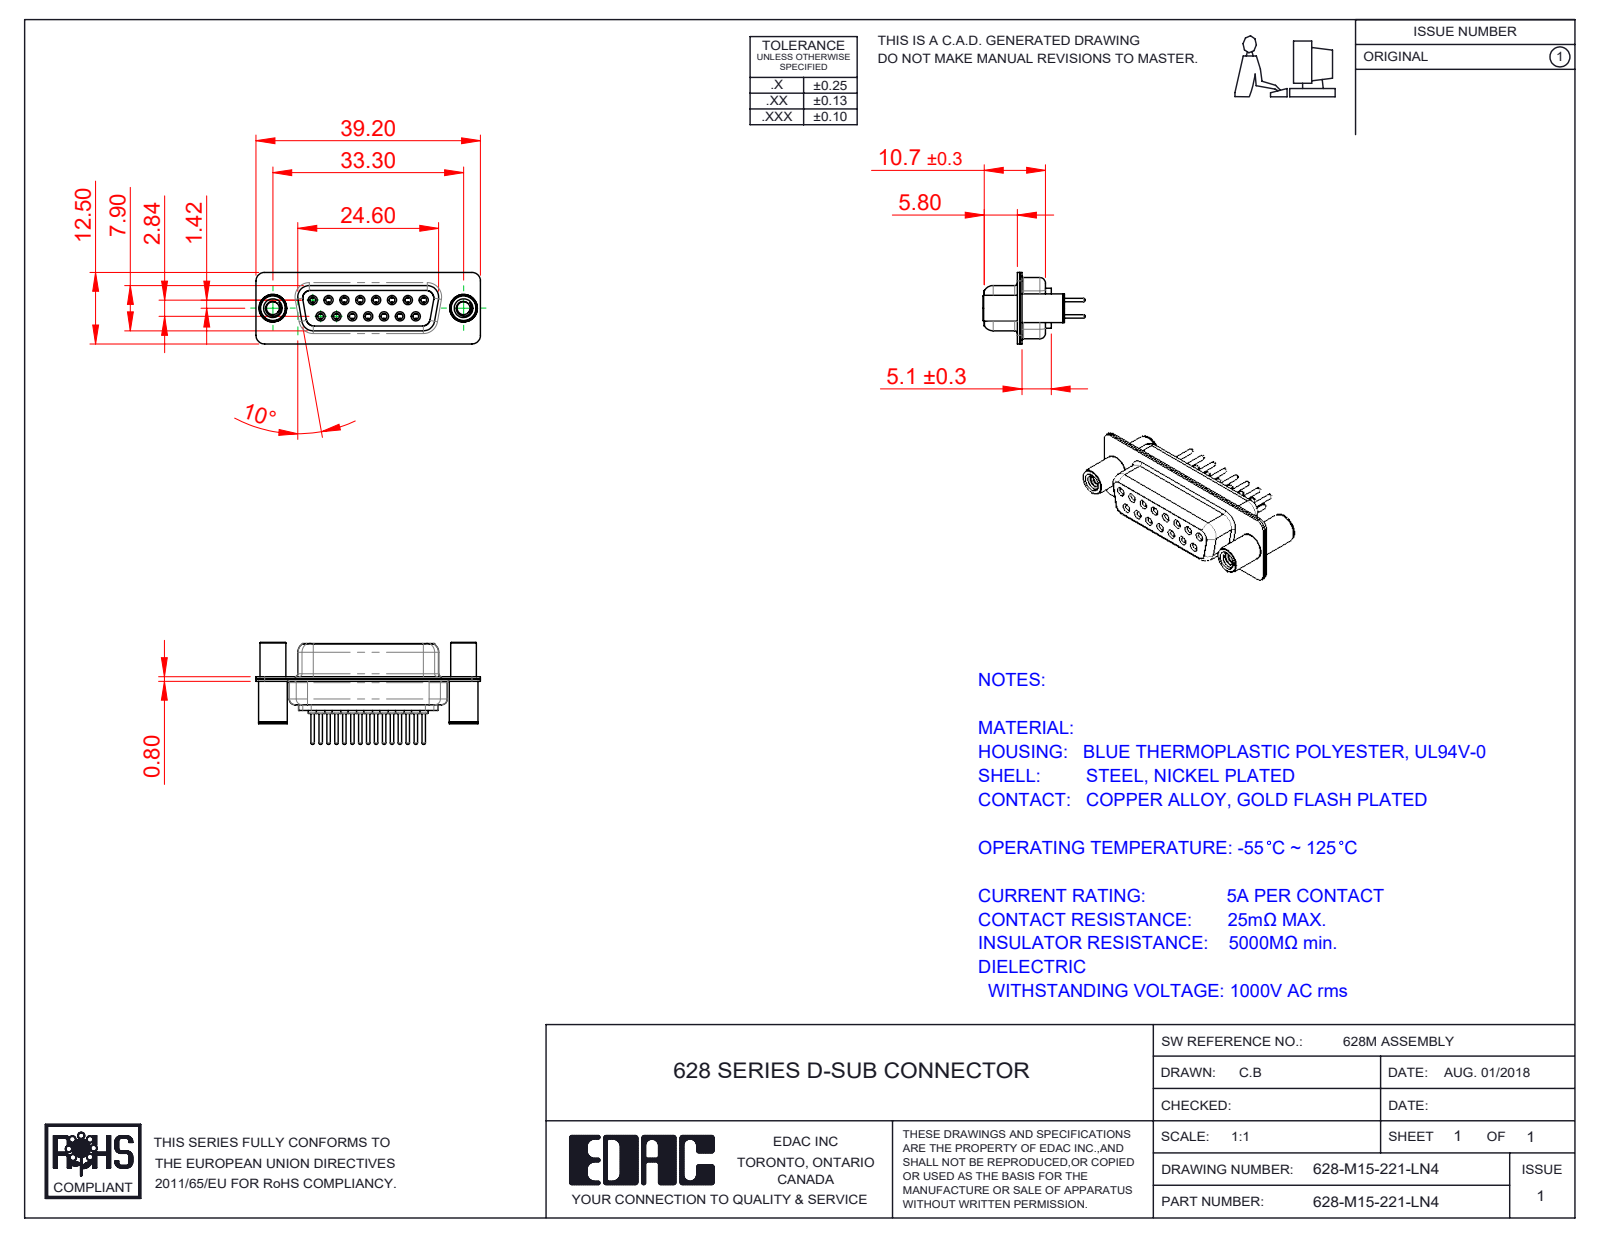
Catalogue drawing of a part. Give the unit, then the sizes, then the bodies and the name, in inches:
Units: inches
Overall size (bounding box): 1.543 × 0.701 × 0.492
Round holes (diameter × count): ⌀0.039 ×15, ⌀0.043 ×15, ⌀0.067 ×15, ⌀0.071 ×15, ⌀0.079 ×15, ⌀0.089 ×2, ⌀0.128 ×2, ⌀0.157 ×2, ⌀0.189 ×2
Round bosses / shafts (diameter × count): ⌀0.087 ×15, ⌀0.063 ×15, ⌀0.059 ×15, ⌀0.024 ×15, ⌀0.197 ×2, ⌀0.193 ×2, ⌀0.177 ×2
Partial cylindrical surfaces — rounded edges, fillets, slot ends (radius × count): R0.059 ×16, R0.079 ×12, R0.053 ×8, R0.063 ×8, R0.01 ×4, R0.02 ×4, R0.024 ×4, R0.026 ×4
Main face-to-face distances: 0.016, 0.055, 0.018, 0.333, 0.071, 0.35, 0.244, 0.278, 0.039, 0.073
Hole centre spacings: 0.124, 0.109, 0.218, 0.327, 0.436, 0.198, 0.198, 0.294
Volume: 0.168 in³ · Surface area: 10.43 in²
Bodies: 20 solids, 1190 faces (298 planar, 474 cylindrical, 418 other)
Part name (STEP PRODUCT): 628M Contact Row 1_21; 628M Shell Rear_15 Contacts; 628M 4-40 Threaded Standoff and Board Spacer; 628M Housing_15 Contacts (+3 more)
STEP written by: SolidWorks 2020 (CONFIG_CONTROL_DESIGN)
